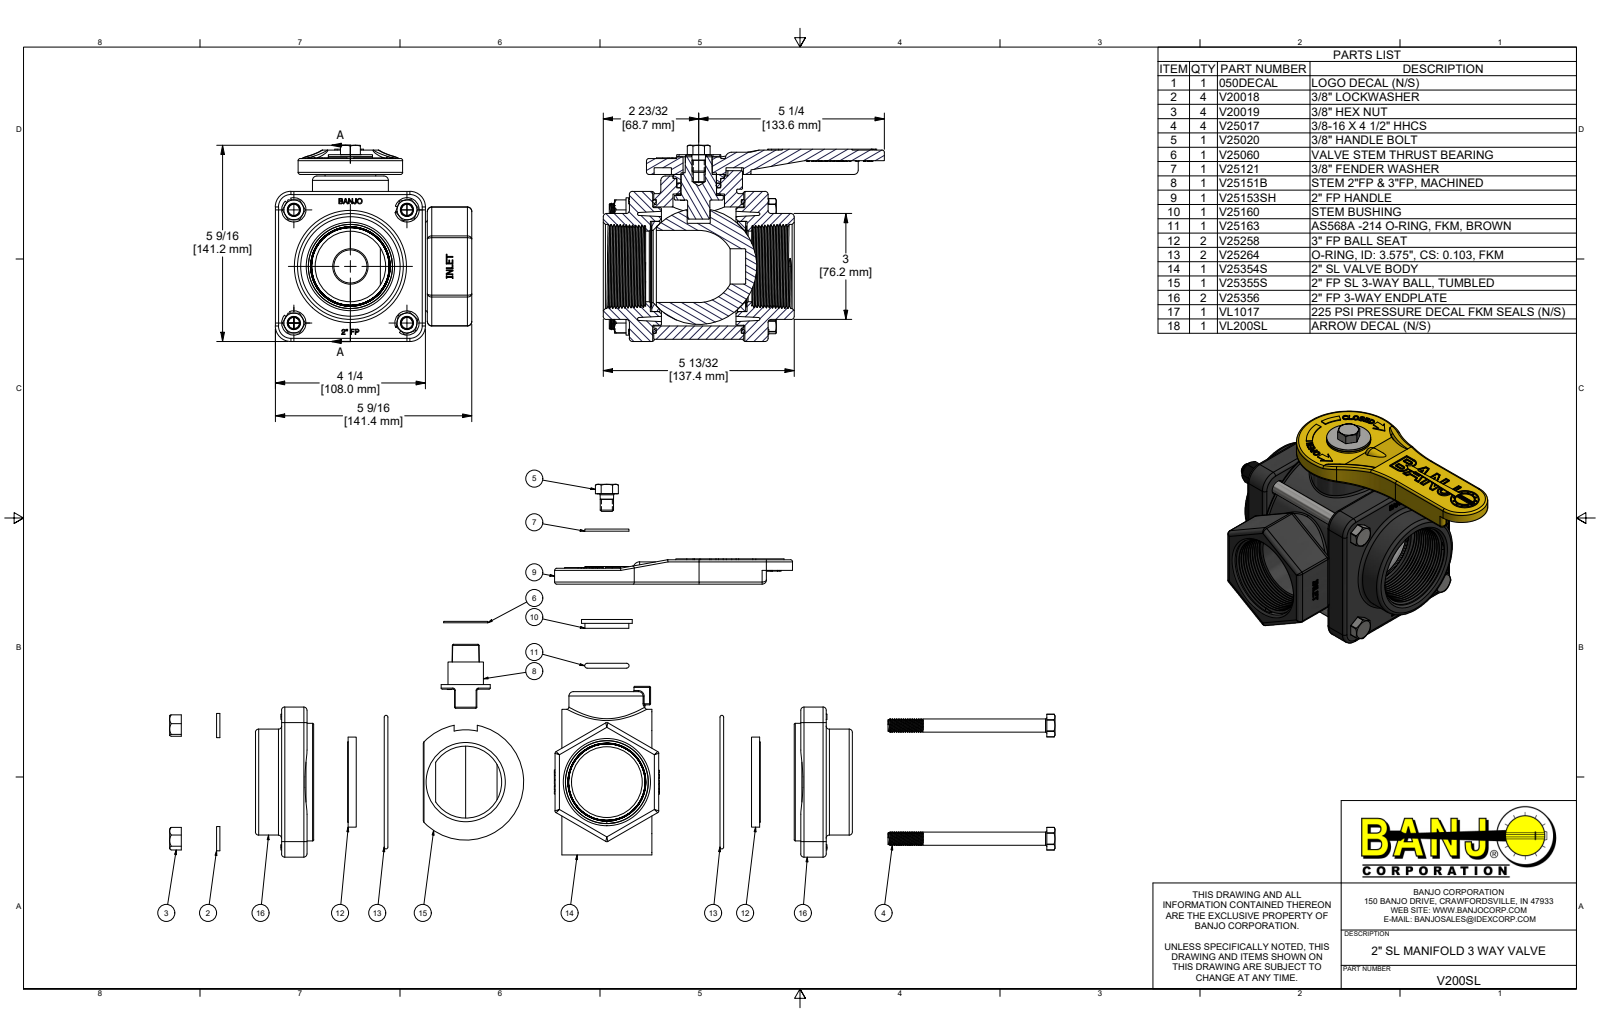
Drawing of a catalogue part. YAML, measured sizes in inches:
part_name: "V200SL; V25354S; V20018; V20019 (+8 more)"
step_written_by: "Autodesk Inventor 2019 (AUTOMOTIVE_DESIGN)"
units: inches
bodies: {solids: 27, faces: 2549, planar: 1420, cylindrical: 468, other: 661}
overall_size: [7.965, 5.565, 5.558]
volume: 57.06
surface_area: 428.9
round_holes:
  - {diameter: 0.17, count: 12}
  - {diameter: 0.307, count: 4}
  - {diameter: 0.385, count: 4}
  - {diameter: 0.438, count: 4}
  - {diameter: 1, count: 2}
  - {diameter: 2, count: 2}
  - {diameter: 2.04, count: 2}
  - {diameter: 0.307, count: 1}
  - {diameter: 0.406, count: 1}
  - {diameter: 0.544, count: 1}
  - {diameter: 0.77, count: 1}
  - {diameter: 1.016, count: 1}
round_bosses_or_shafts:
  - {diameter: 0.324, count: 60}
  - {diameter: 0.375, count: 5}
  - {diameter: 0.687, count: 4}
  - {diameter: 4.125, count: 1}
  - {diameter: 3.5, count: 1}
  - {diameter: 3.33, count: 1}
  - {diameter: 3, count: 1}
  - {diameter: 2.96, count: 1}
partial_cylinders:
  - {radius: 0.09, count: 16}
  - {radius: 0.03, count: 12}
  - {radius: 0.06, count: 12}
  - {radius: 0.125, count: 12}
  - {radius: 0.032, count: 10}
  - {radius: 0.062, count: 8}
  - {radius: 0.162, count: 8}
  - {radius: 0.12, count: 5}
face_to_face_distances: [0.66, 3.27, 3.93, 4.25, 0.03, 0.69, 3.24, 2.58, 0.06, 2.61]
hole_center_spacings: [1.977, 2.796, 3.82, 1.023, 1.133, 2.136, 3.007, 3.424]
